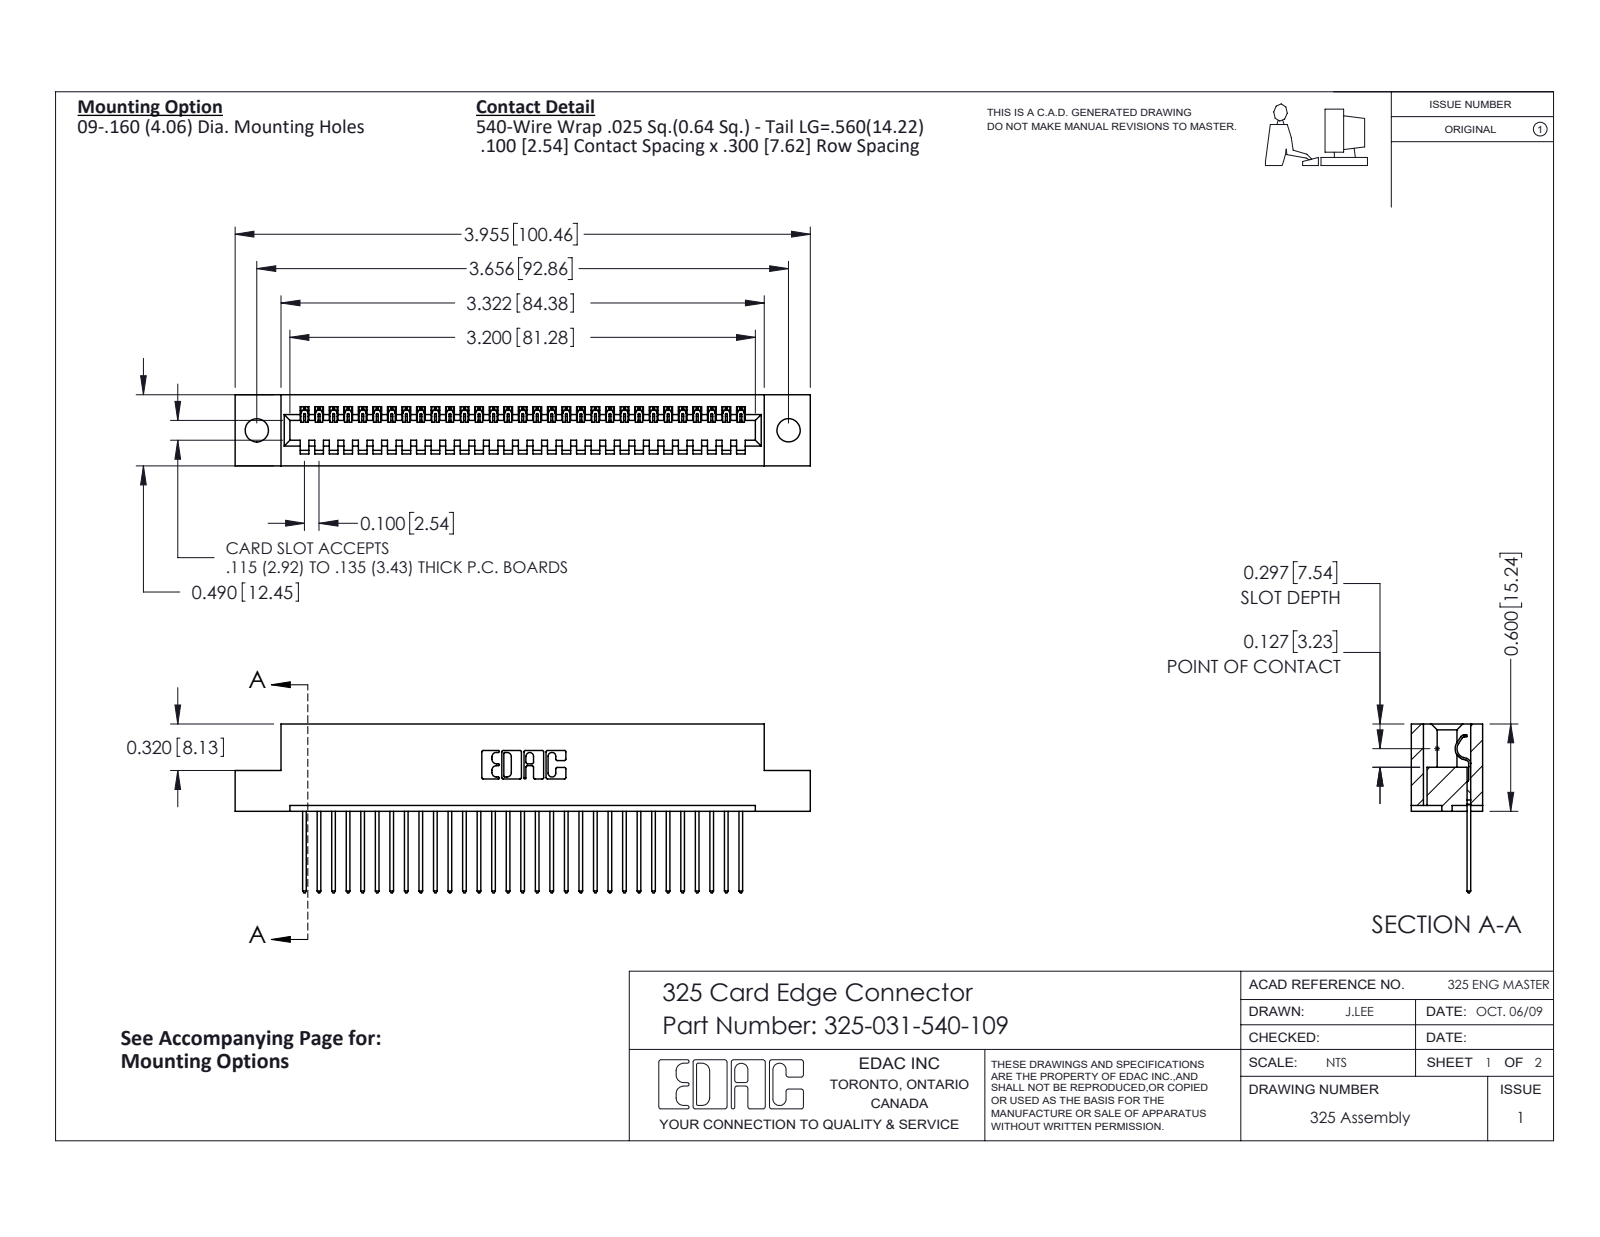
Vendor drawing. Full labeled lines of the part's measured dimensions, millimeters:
Part name (STEP PRODUCT): 325-292-001_325-293-140; 325-031-540-109; 325 Part_.160 TH
STEP written by: SolidWorks 2016 (CONFIG_CONTROL_DESIGN)
Units: millimetres
Bodies: 32 solids, 1912 faces (1372 planar, 540 cylindrical, 0 other)
Overall size (bounding box): 100.5 × 29.5 × 12.4
Volume: 12 500 mm³ · Surface area: 13 650 mm²
Round holes (diameter × count): ⌀4.1 ×2
Partial cylindrical surfaces — rounded edges, fillets, slot ends (radius × count): R0.2 ×62, R0.3 ×62, R0.3 ×22, R0.2 ×6, R0.8 ×6, R0.7 ×3, R0.4 ×1, R0.6 ×1
Main face-to-face distances: 2.1, 10.3, 7.6, 12.4, 2.7, 9.7, 0.6, 8.3, 1, 2.5
Hole centre spacings: 92.9
